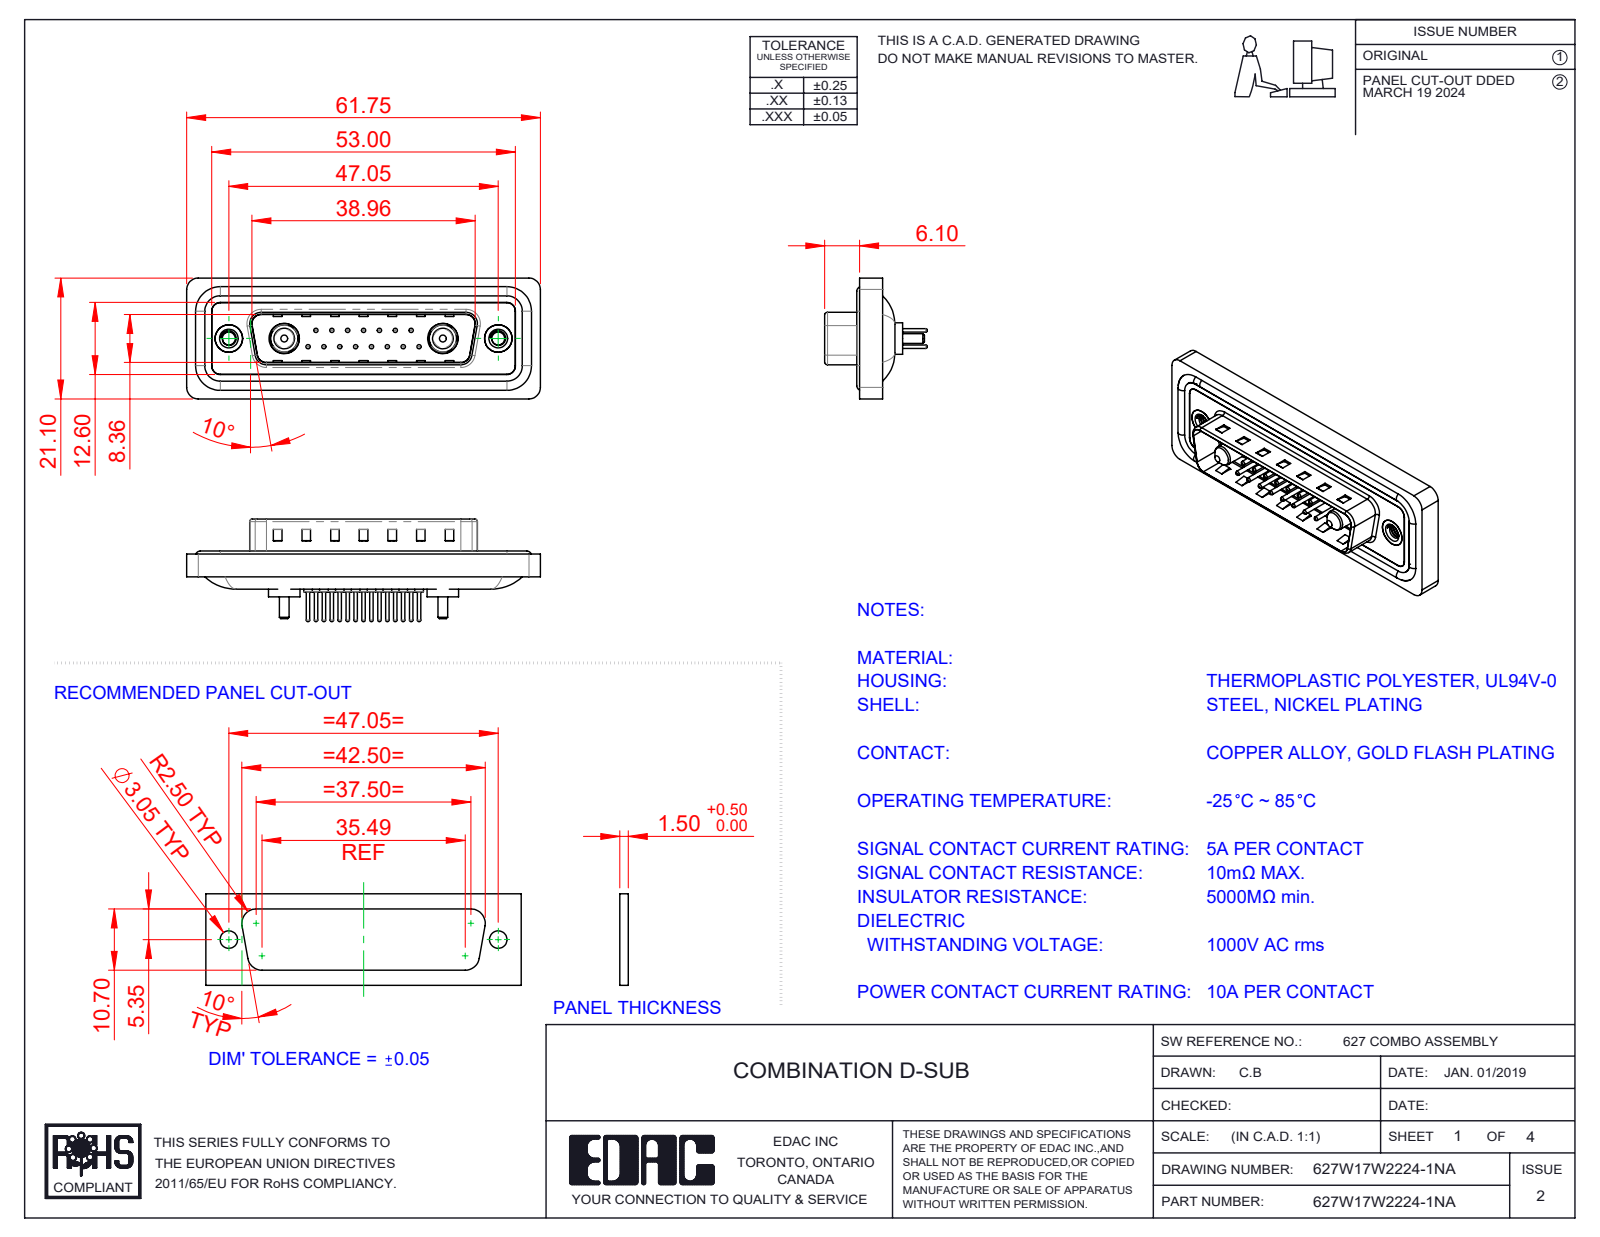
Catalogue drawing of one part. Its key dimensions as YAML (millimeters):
part_name: "627Combo Contact Row 2_24; 627Combo Housing_17W2; Power Pin_10A S; 627Combo Threaded Rivet_A (+5 more)"
step_written_by: "SolidWorks 2023 (CONFIG_CONTROL_DESIGN)"
units: millimeters
bodies: {solids: 26, faces: 1114, planar: 334, cylindrical: 438, other: 342}
overall_size: [61.75, 21.1, 17.9]
volume: 7239
surface_area: 11886
round_holes:
  - {diameter: 0.75, count: 15}
  - {diameter: 1.6, count: 15}
  - {diameter: 2, count: 15}
  - {diameter: 2.26, count: 2}
  - {diameter: 4, count: 2}
  - {diameter: 4.8, count: 2}
  - {diameter: 4.85, count: 2}
  - {diameter: 5, count: 2}
  - {diameter: 5.3, count: 2}
round_bosses_or_shafts:
  - {diameter: 1.5, count: 15}
  - {diameter: 0.6, count: 15}
  - {diameter: 1.6, count: 4}
  - {diameter: 5.5, count: 2}
  - {diameter: 5.2, count: 2}
  - {diameter: 4.9, count: 2}
  - {diameter: 4.75, count: 2}
  - {diameter: 3.75, count: 2}
partial_cylinders:
  - {radius: 1.5, count: 22}
  - {radius: 2, count: 18}
  - {radius: 0.5, count: 8}
  - {radius: 1.6, count: 8}
  - {radius: 0.25, count: 4}
  - {radius: 0.6, count: 4}
  - {radius: 0.65, count: 4}
  - {radius: 0.9, count: 4}
face_to_face_distances: [0.4, 1.5, 1.1, 1.6, 0.5, 3.1, 2.9, 0.82, 9.58, 4.1]
hole_center_spacings: [3.16, 2.77, 5.54, 8.31, 5.04, 7.49, 11.08, 5.03]
